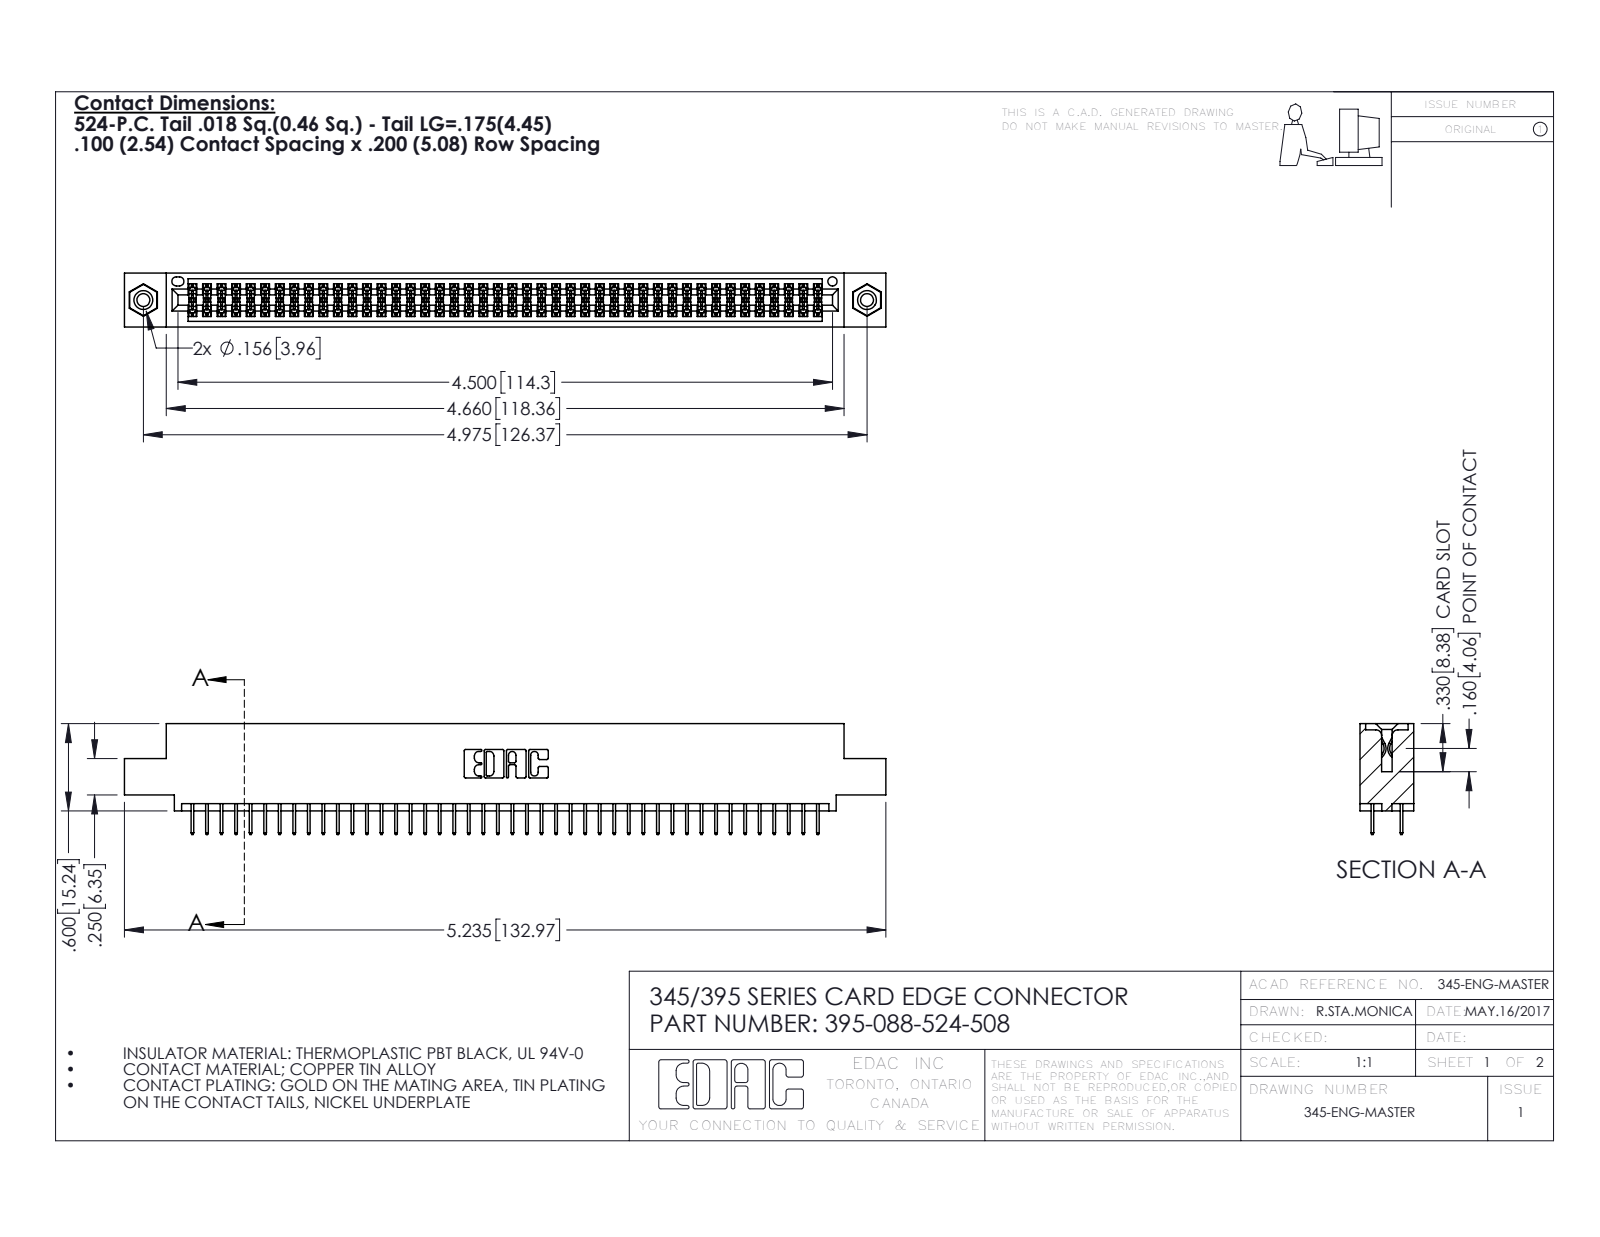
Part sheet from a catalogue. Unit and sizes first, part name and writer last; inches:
Units: inches
Overall size (bounding box): 5.235 × 0.762 × 0.37
Round holes (diameter × count): ⌀0.089 ×2, ⌀0.125 ×2, ⌀0.156 ×2, ⌀0.064 ×1
Round bosses / shafts (diameter × count): ⌀0.155 ×2
Partial cylindrical surfaces — rounded edges, fillets, slot ends (radius × count): R0.006 ×132, R0.01 ×22, R0.007 ×6, R0.031 ×6, R0.026 ×3, R0.014 ×2, R0.019 ×2, R0.022 ×2
Main face-to-face distances: 0.072, 0.298, 0.2, 0.37, 0.098, 0.272, 0.025, 0.225, 0.072, 0.175
Hole centre spacings: 0.27, 4.739, 4.975
Volume: 0.776 in³ · Surface area: 28.83 in²
Bodies: 91 solids, 4942 faces (3548 planar, 1378 cylindrical, 16 other)
Part name (STEP PRODUCT): 345-292-001_345-293-124; 345-250-001_345-250-003-102; 395-088-524-508; 345 Part_0.110 Offset - 0.156 Dia-TI
STEP written by: SolidWorks 2016 (CONFIG_CONTROL_DESIGN)
